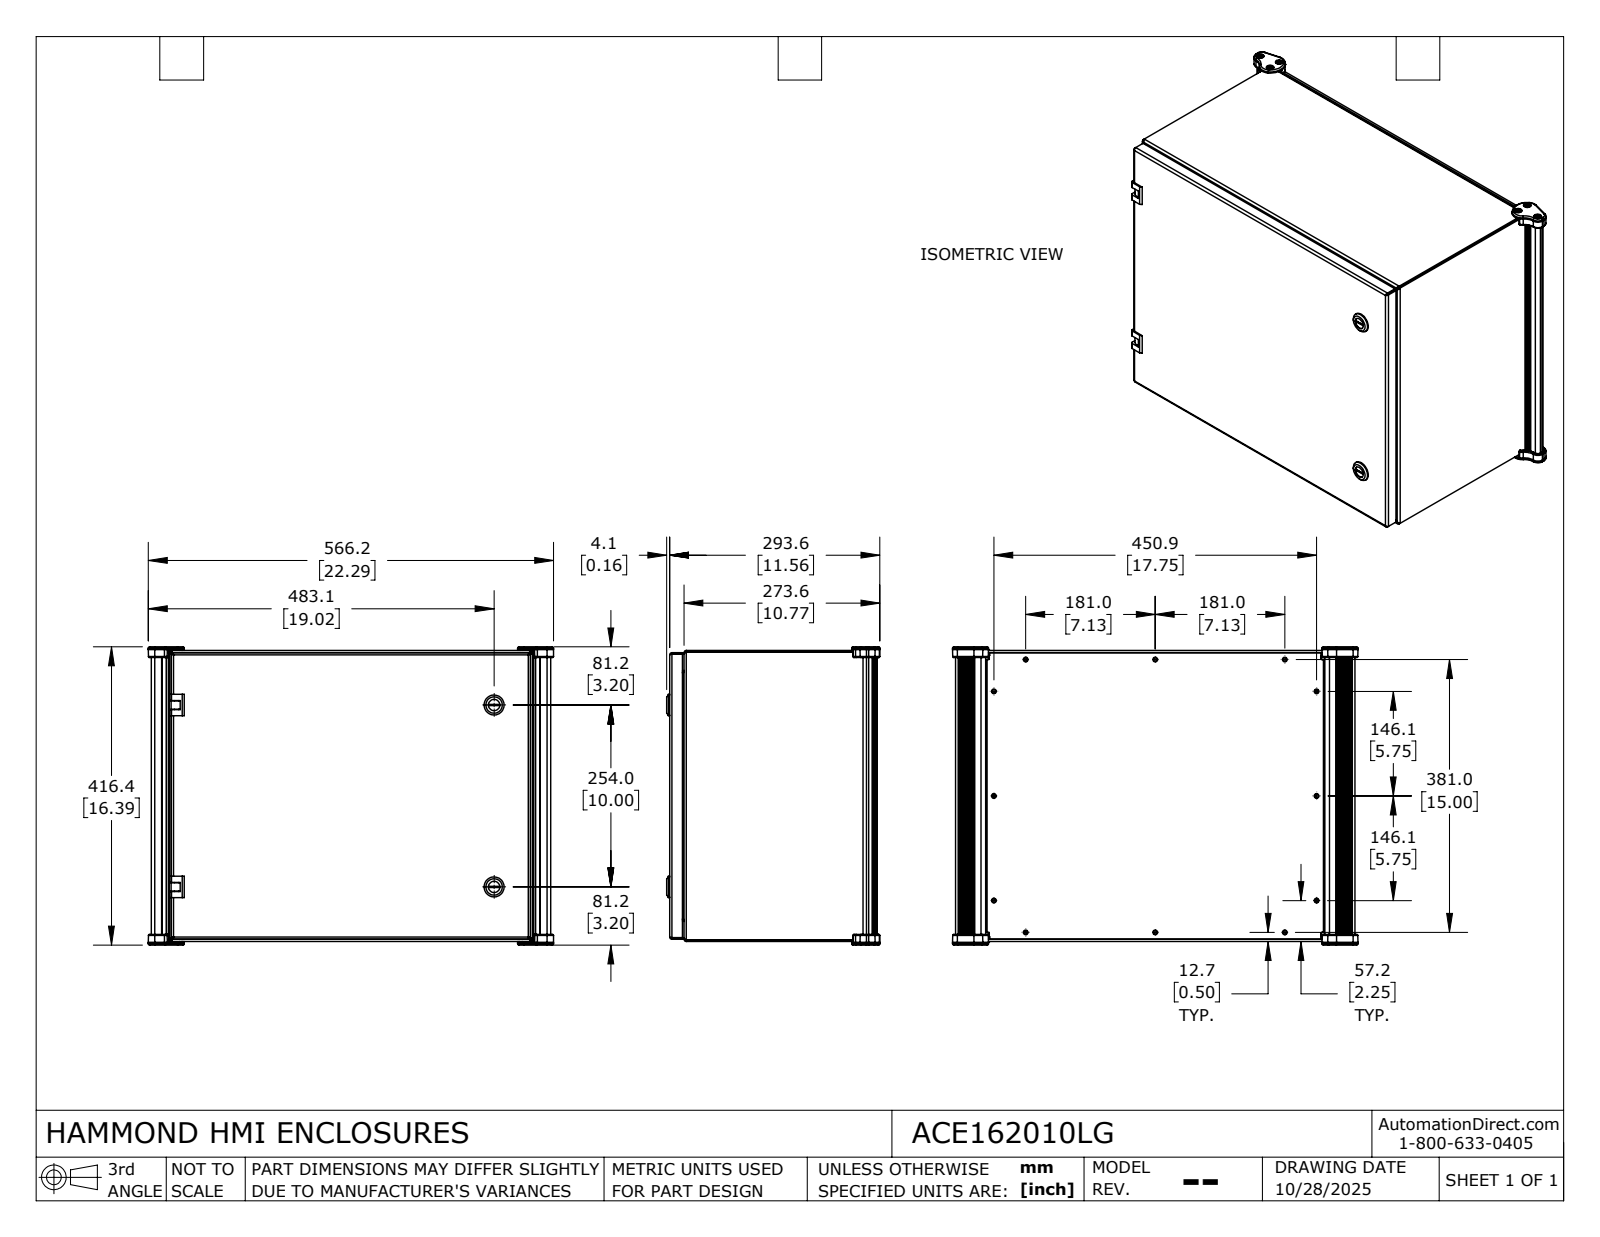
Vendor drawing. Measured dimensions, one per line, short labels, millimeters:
name: ACE162010LG
written by: SolidWorks 2024 (AUTOMOTIVE_DESIGN)
unit: mm
bodies: 99 solids, 2540 faces (1210 planar, 865 cylindrical, 465 other)
size: 566.22 × 416.43 × 297.66
volume: 3 025 000 mm³; area: 2 641 000 mm²
holes: 14× ⌀3.97, 14× ⌀5.94, 12× ⌀4.83, 6× ⌀5.2, 6× ⌀10.5, 5× ⌀4.98, 4× ⌀4.04, 4× ⌀10.32, 2× ⌀4.06, 2× ⌀5, 2× ⌀5.89, 2× ⌀6.35
bosses: 12× ⌀6.5, 6× ⌀6.35, 6× ⌀4.83, 6× ⌀3.79, 5× ⌀5.99, 4× ⌀9.53, 4× ⌀8.38, 2× ⌀27.94
rounds: 38× R0.25, 30× R1.5, 20× R1.03, 20× R3.09, 16× R0.4, 16× R0.75, 16× R1.27, 14× R1
face distances: 2.06, 404.34, 3.17, 3.18, 275.1, 277.16, 278.28, 280.34, 5.23, 2.05
hole spacings: 203.2, 62.86, 146.05, 195.62, 242.94, 339.47, 405.07, 408.82
